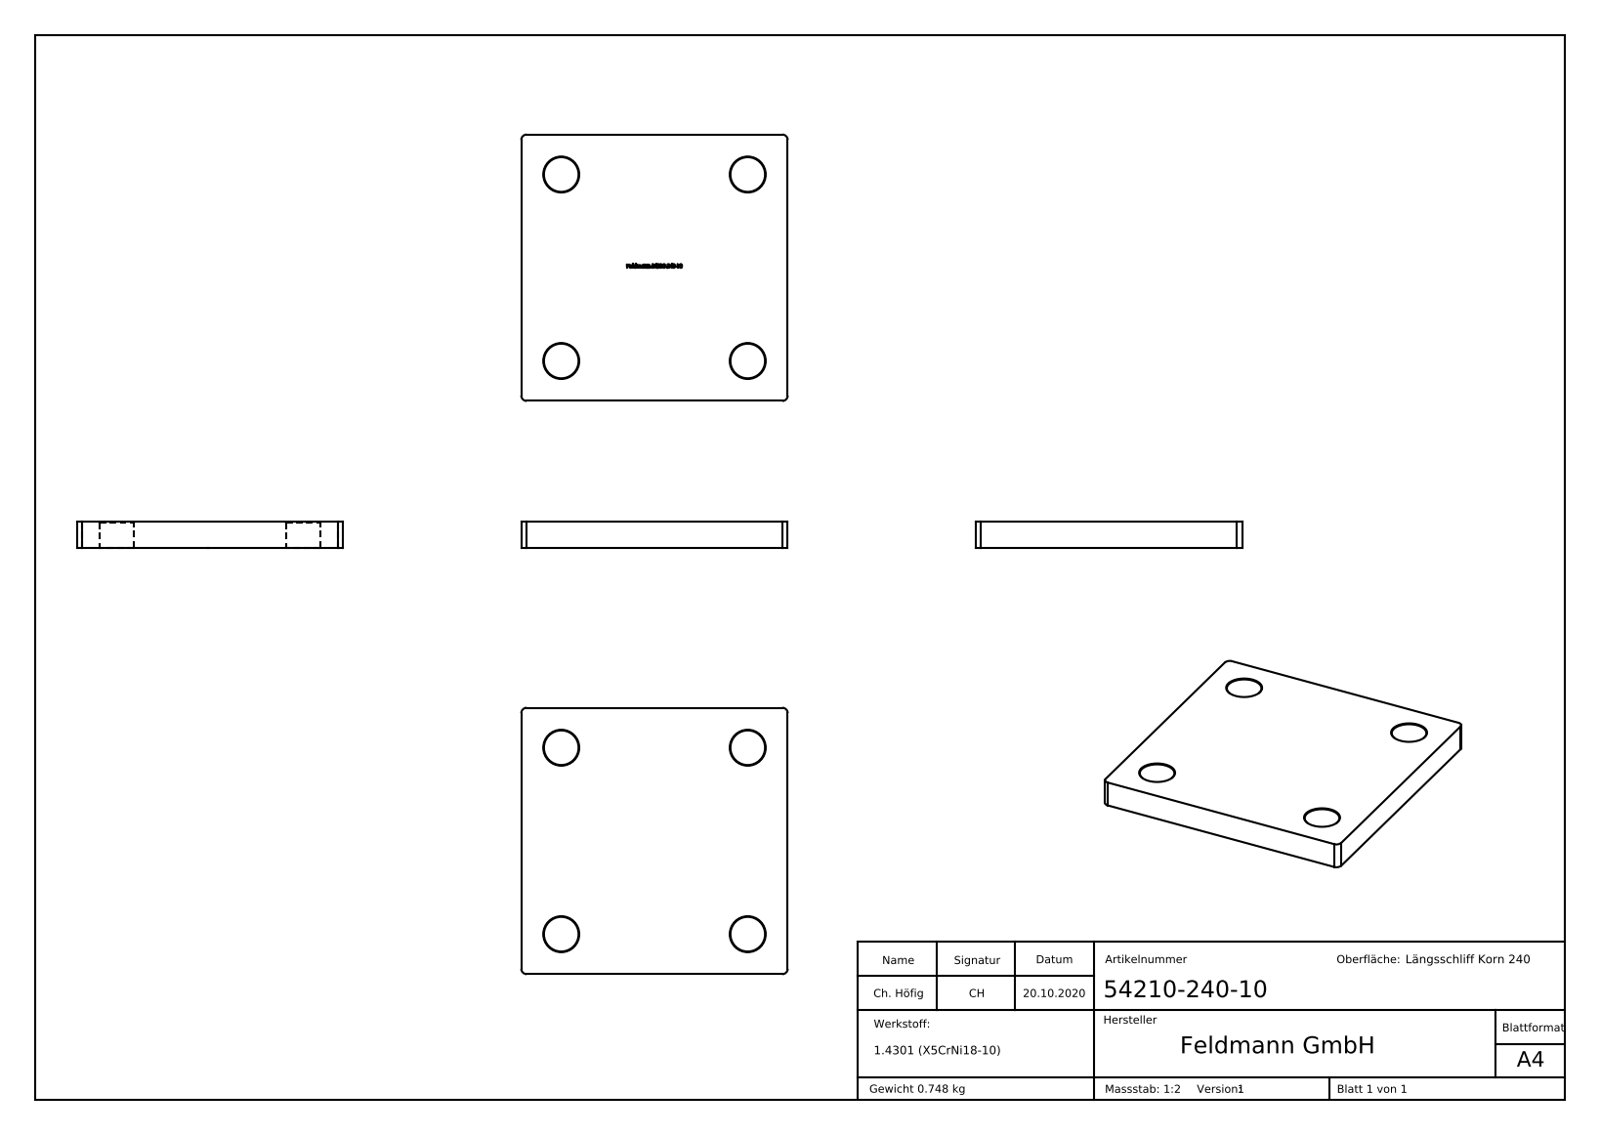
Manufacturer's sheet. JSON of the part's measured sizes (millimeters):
{"part_name": "54210-240-10", "step_written_by": "SolidWorks 2018 (CONFIG_CONTROL_DESIGN)", "units": "millimeters", "bodies": {"solids": 1, "faces": 275, "planar": 152, "cylindrical": 12, "other": 111}, "overall_size": [100, 100, 10], "volume_mm3": 94645, "surface_area_mm2": 24494, "round_holes": [[13, 4]], "partial_cylinders_radius": [[2, 4]], "face_to_face_distances": [10, 100, 9.9, 50, 0.44, 0.88, 10.74, 17.05, 6.31, 2.02], "hole_center_spacings": [70, 98.99]}
